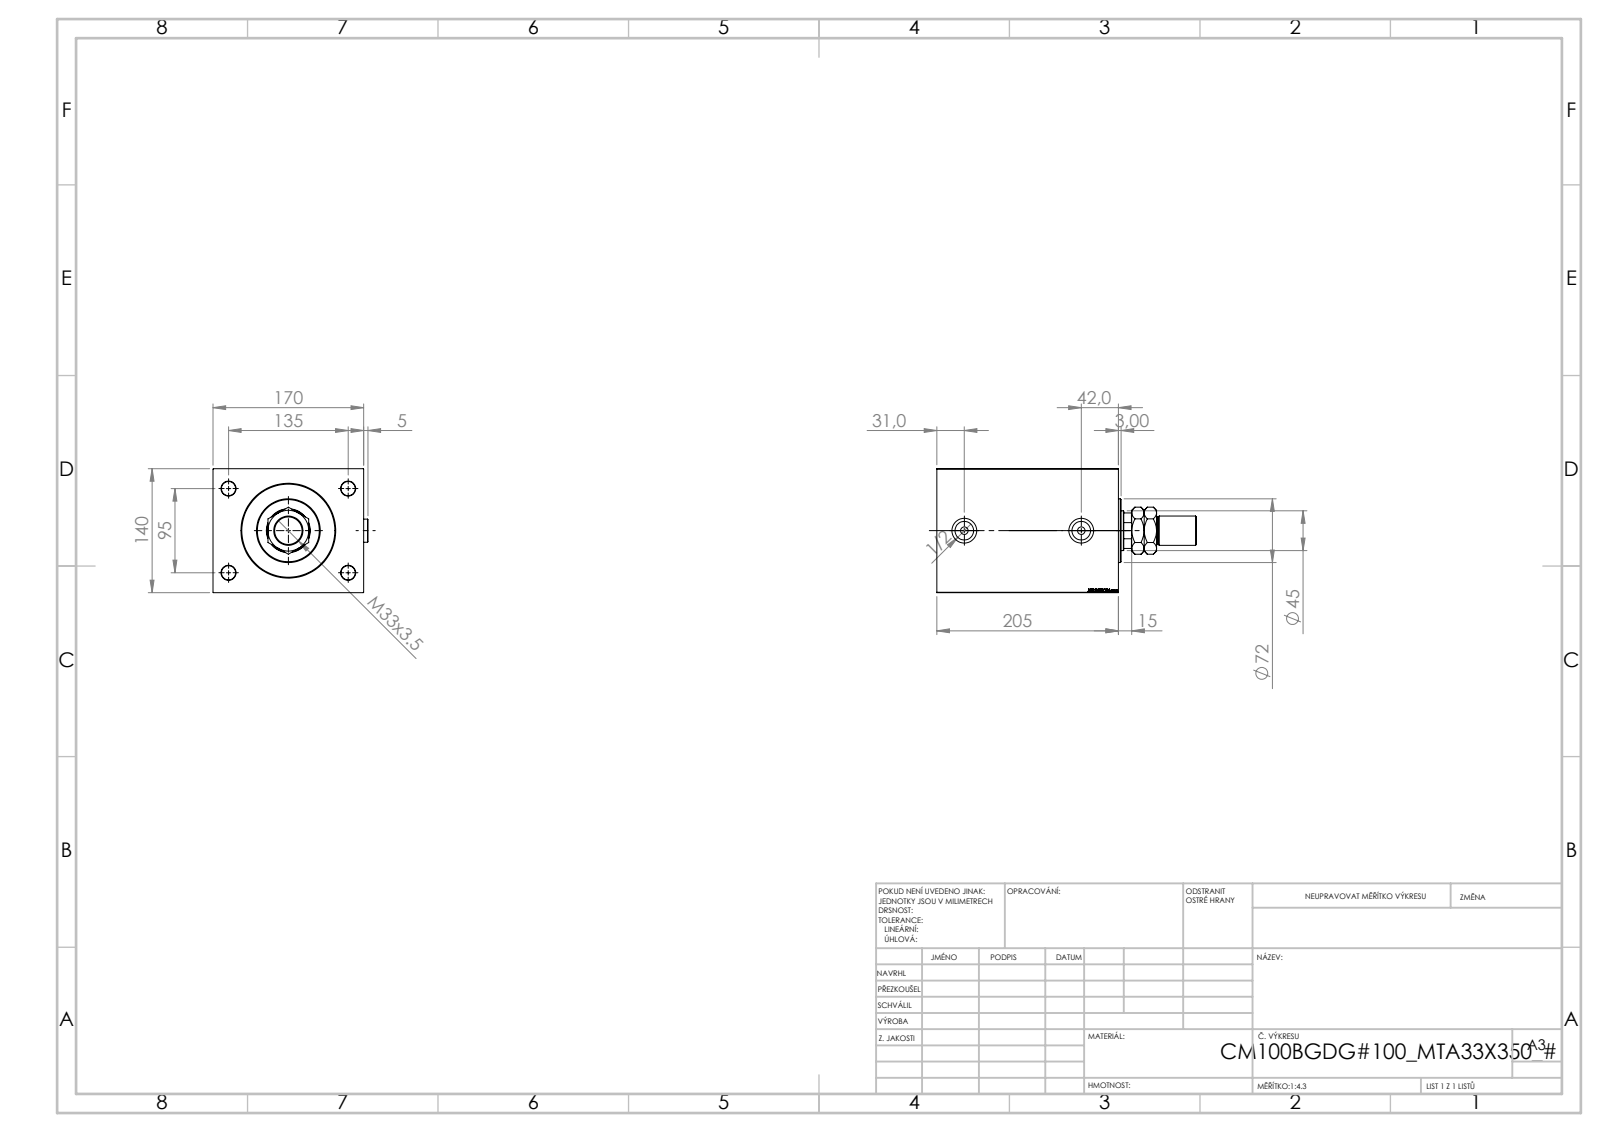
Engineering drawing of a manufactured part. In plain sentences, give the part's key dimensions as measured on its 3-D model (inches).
The part is named "V450CM_B_Body; V450CM_B_VCP; MTA; Zatka_OIL_PORT (+1 more)". Its 3-D file was written by "SolidWorks 2019 (CONFIG_CONTROL_DESIGN)". It is 6 solids with 987 faces: 451 planar, 76 cylindrical and 460 other. Overall it measures 11.535 by 6.886 by 5.512 inches. Its volume is 260.5 cubic inches and its surface area 533.4 square inches. Round holes: 4 of diameter 0.63, 2 of diameter 0.335, 2 of diameter 0.825, 2 of diameter 1.102, 1 of diameter 1.24, 1 of diameter 1.772, 1 of diameter 1.909, 1 of diameter 1.949, 1 of diameter 3.937, 1 of diameter 4.016, 1 of diameter 4.134. Round bosses or shafts: 2 of diameter 1.024, 1 of diameter 2.835, 1 of diameter 1.299, 1 of diameter 1.22. Partial cylindrical surfaces (rounded edges, fillets, slot ends): 1 of radius 0.866. The main face-to-face distances are 5.512, 6.693, 8.071, 7.047, 1.024, 0.591, 6.457, 7.48, 3.543, 2.52. The hole center spacings are 3.25, 3.74, 5.315, 6.499, 5.197.
